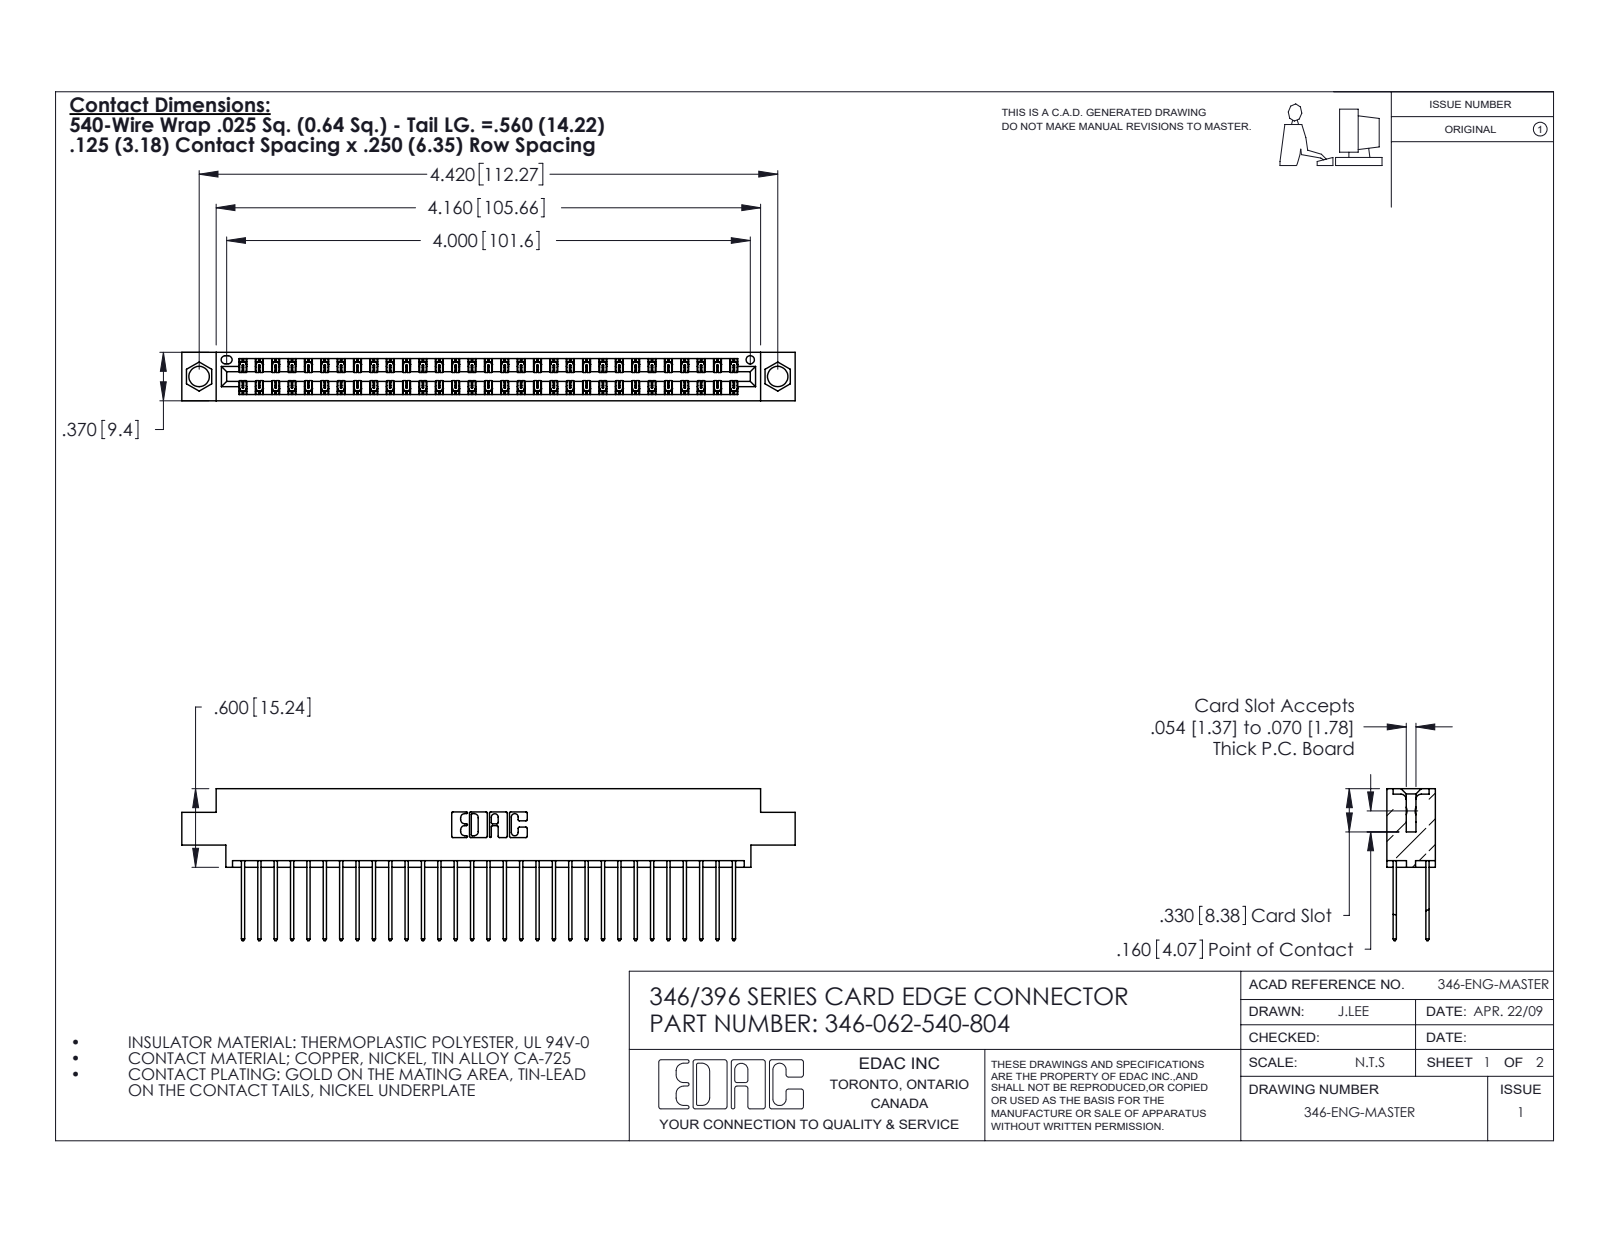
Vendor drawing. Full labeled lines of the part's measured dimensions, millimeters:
Part name (STEP PRODUCT): 346 Part_0.170 Offset - 0.156 Dia-TH; 346-062-540-804; 345-292-001_345-293-140
STEP written by: SolidWorks 2020 (CONFIG_CONTROL_DESIGN)
Units: millimetres
Bodies: 63 solids, 3364 faces (2264 planar, 1100 cylindrical, 0 other)
Overall size (bounding box): 119 × 29.5 × 9.4
Volume: 11 500 mm³ · Surface area: 16 760 mm²
Round holes (diameter × count): ⌀4 ×2, ⌀1.6 ×1
Partial cylindrical surfaces — rounded edges, fillets, slot ends (radius × count): R0.2 ×93, R0.3 ×62, R0.3 ×22, R0.2 ×6, R0.8 ×6, R0.7 ×3, R0.4 ×2, R0.6 ×2
Main face-to-face distances: 1.2, 8.2, 6.4, 9.4, 1.8, 7.6, 0.6, 7, 5.6, 3.8
Hole centre spacings: 6.2, 107, 112.3
